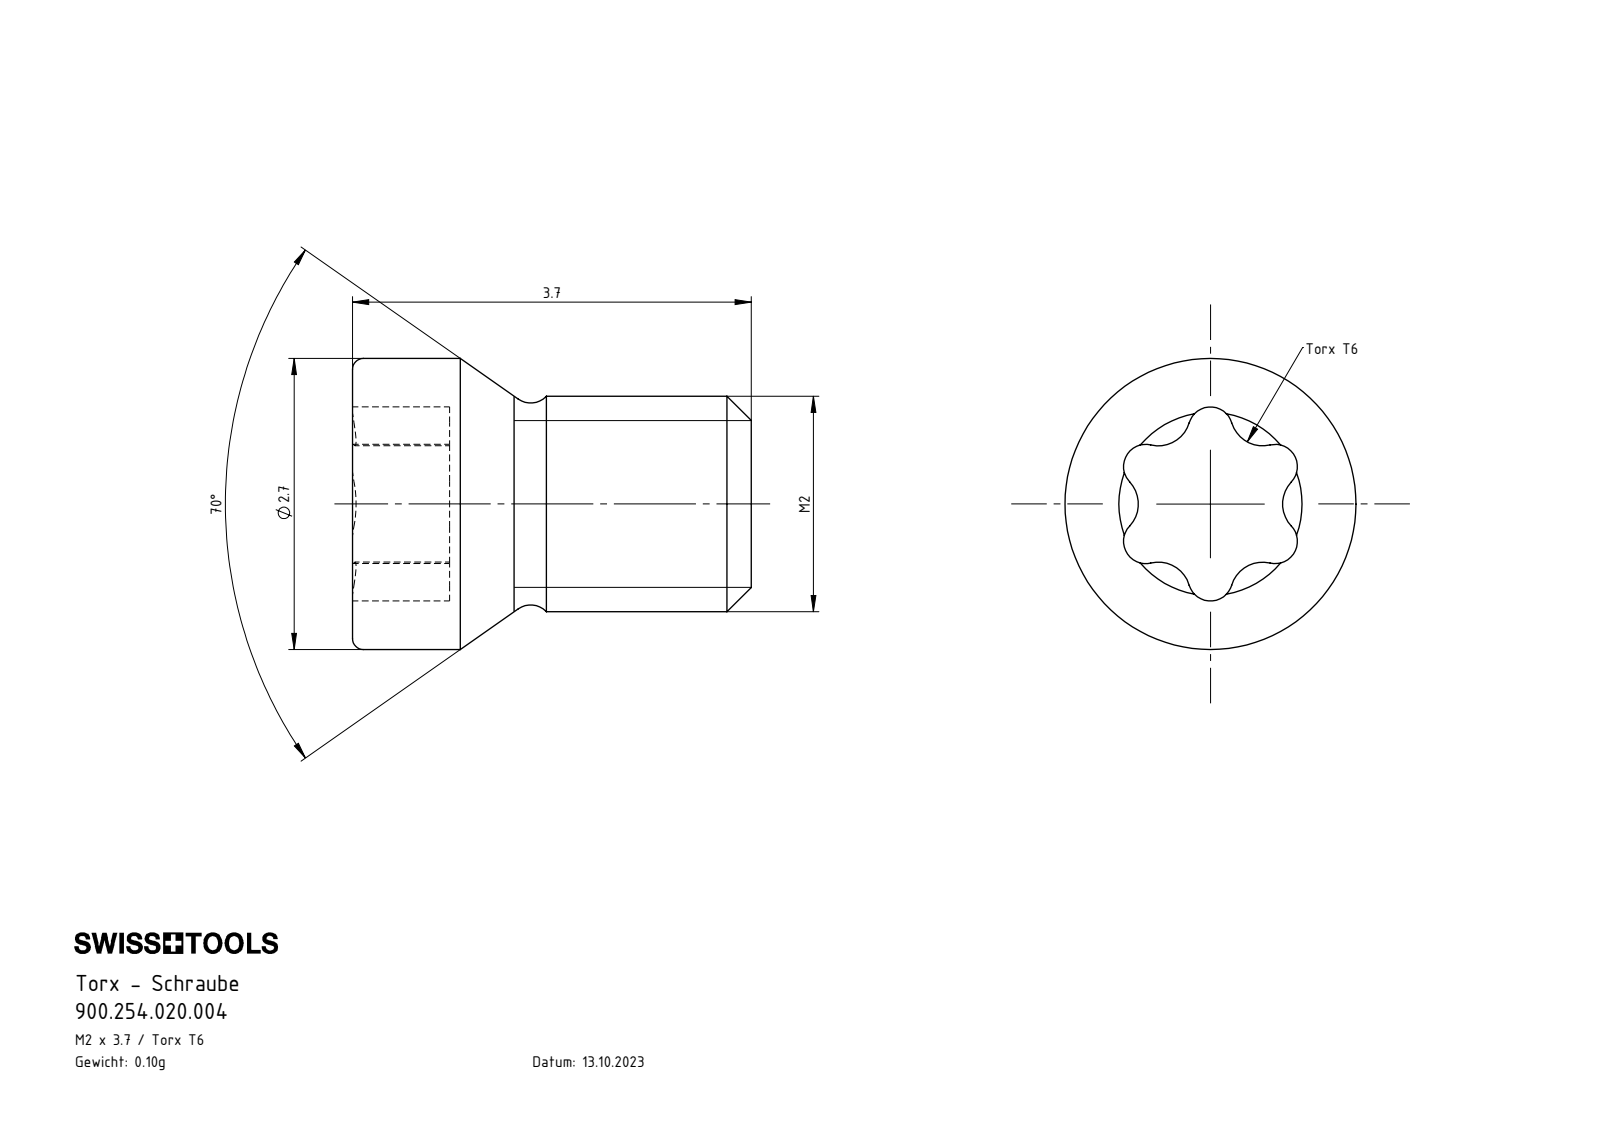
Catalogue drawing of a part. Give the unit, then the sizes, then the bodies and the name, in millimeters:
Units: millimetres
Overall size (bounding box): 3.7 × 2.7 × 2.7
Round bosses / shafts (diameter × count): ⌀2.7 ×1, ⌀2 ×1
Partial cylindrical surfaces — rounded edges, fillets, slot ends (radius × count): R0.21 ×6, R0.3 ×6
Main face-to-face distances: 0.9, 3.7, 2.8
Volume: 13 mm³ · Surface area: 40 mm²
Bodies: 1 solid, 41 faces (3 planar, 19 cylindrical, 19 other)
Part name (STEP PRODUCT): 900.254.020.004
STEP written by: SolidWorks 2022 (AUTOMOTIVE_DESIGN)
